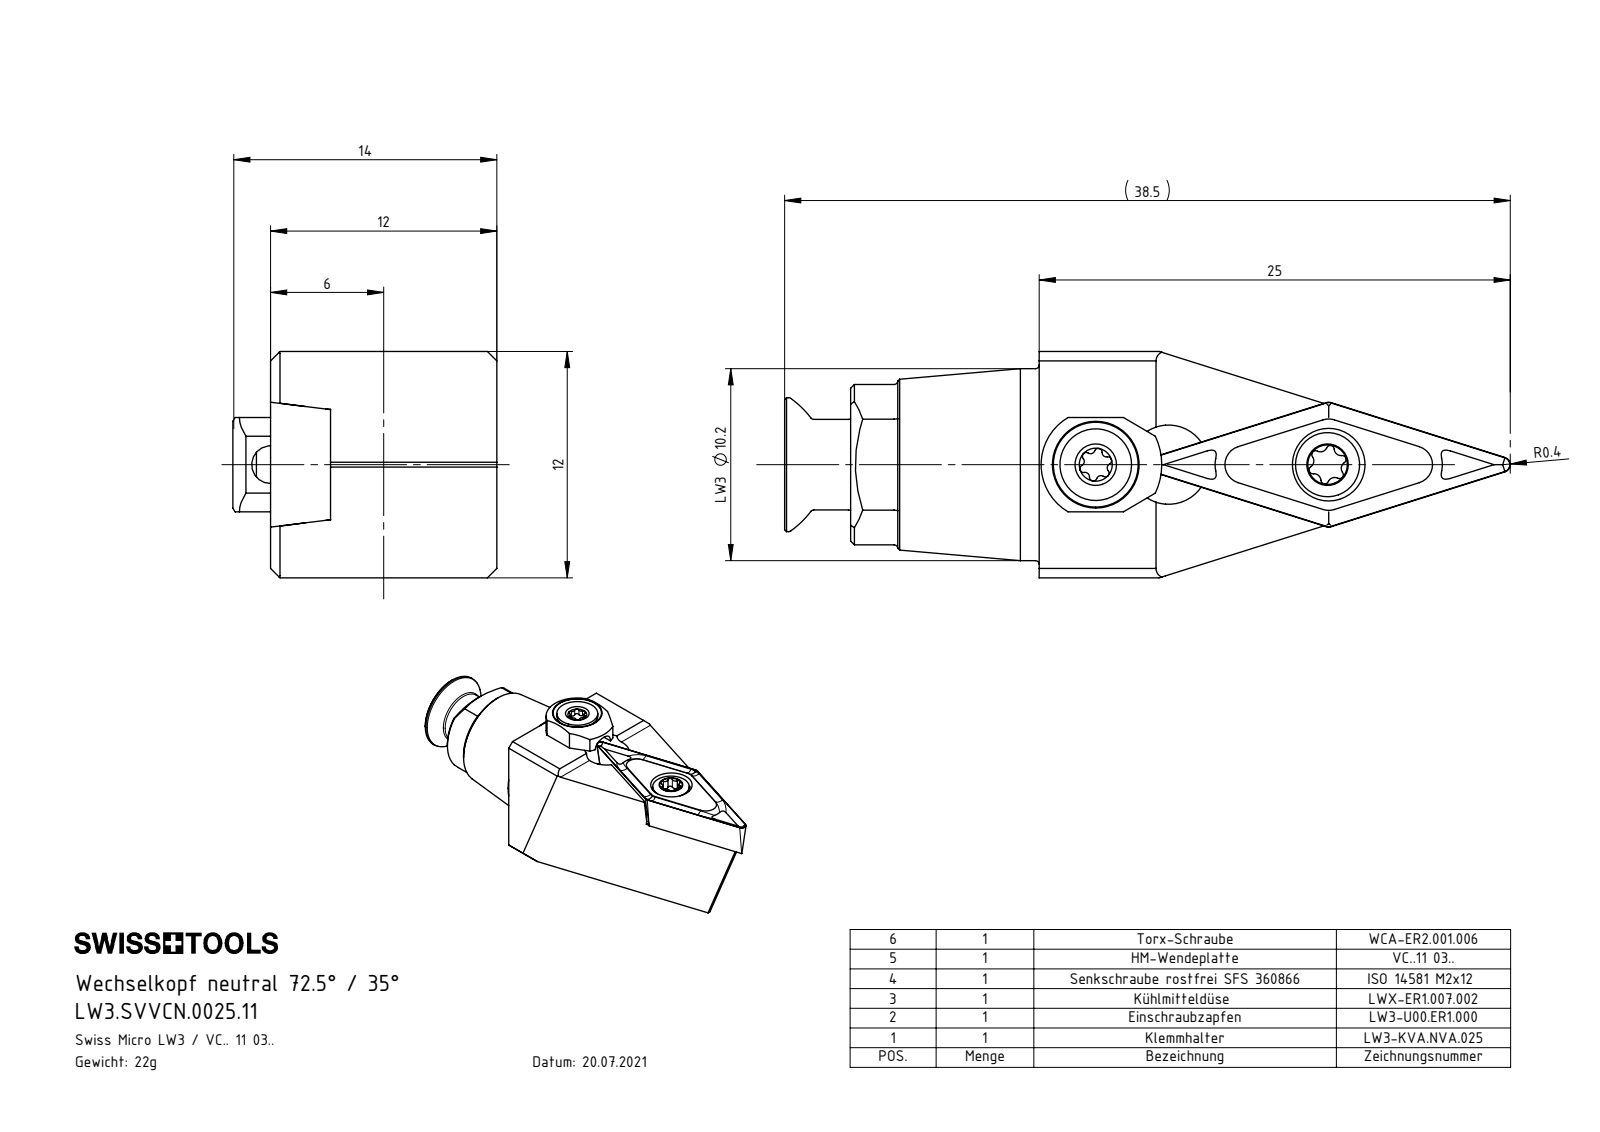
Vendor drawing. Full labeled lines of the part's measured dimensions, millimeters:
Part name (STEP PRODUCT): ISO 14581 - M2x12; LWX-ER1.007.002; VCGT110304; WCA-ER2.001.006_A (+3 more)
STEP written by: SolidWorks 2022 (CONFIG_CONTROL_DESIGN)
Units: millimetres
Bodies: 6 solids, 254 faces (70 planar, 78 cylindrical, 106 other)
Overall size (bounding box): 38.38 × 14 × 12
Volume: 2 592 mm³ · Surface area: 2 438 mm²
Round holes (diameter × count): ⌀1.6 ×1, ⌀2 ×1, ⌀2.05 ×1, ⌀2.5 ×1, ⌀2.8 ×1, ⌀3 ×1, ⌀3.85 ×1, ⌀4.2 ×1, ⌀5.5 ×1
Round bosses / shafts (diameter × count): ⌀10.18 ×1, ⌀6.9 ×1, ⌀6 ×1, ⌀5 ×1, ⌀4.8 ×1, ⌀3.8 ×1, ⌀3.4 ×1, ⌀2.5 ×1
Partial cylindrical surfaces — rounded edges, fillets, slot ends (radius × count): R0.2 ×8, R0.21 ×6, R0.24 ×6, R0.36 ×4, R0.36 ×2, R0.5 ×1, R1 ×1, R2.9 ×1
Main face-to-face distances: 12, 8.82, 3.18, 2, 11.5, 2.68, 0.5, 2.5, 13.4, 11.4
Hole centre spacings: 3.86, 8.43, 8.5, 12.29, 12.36
